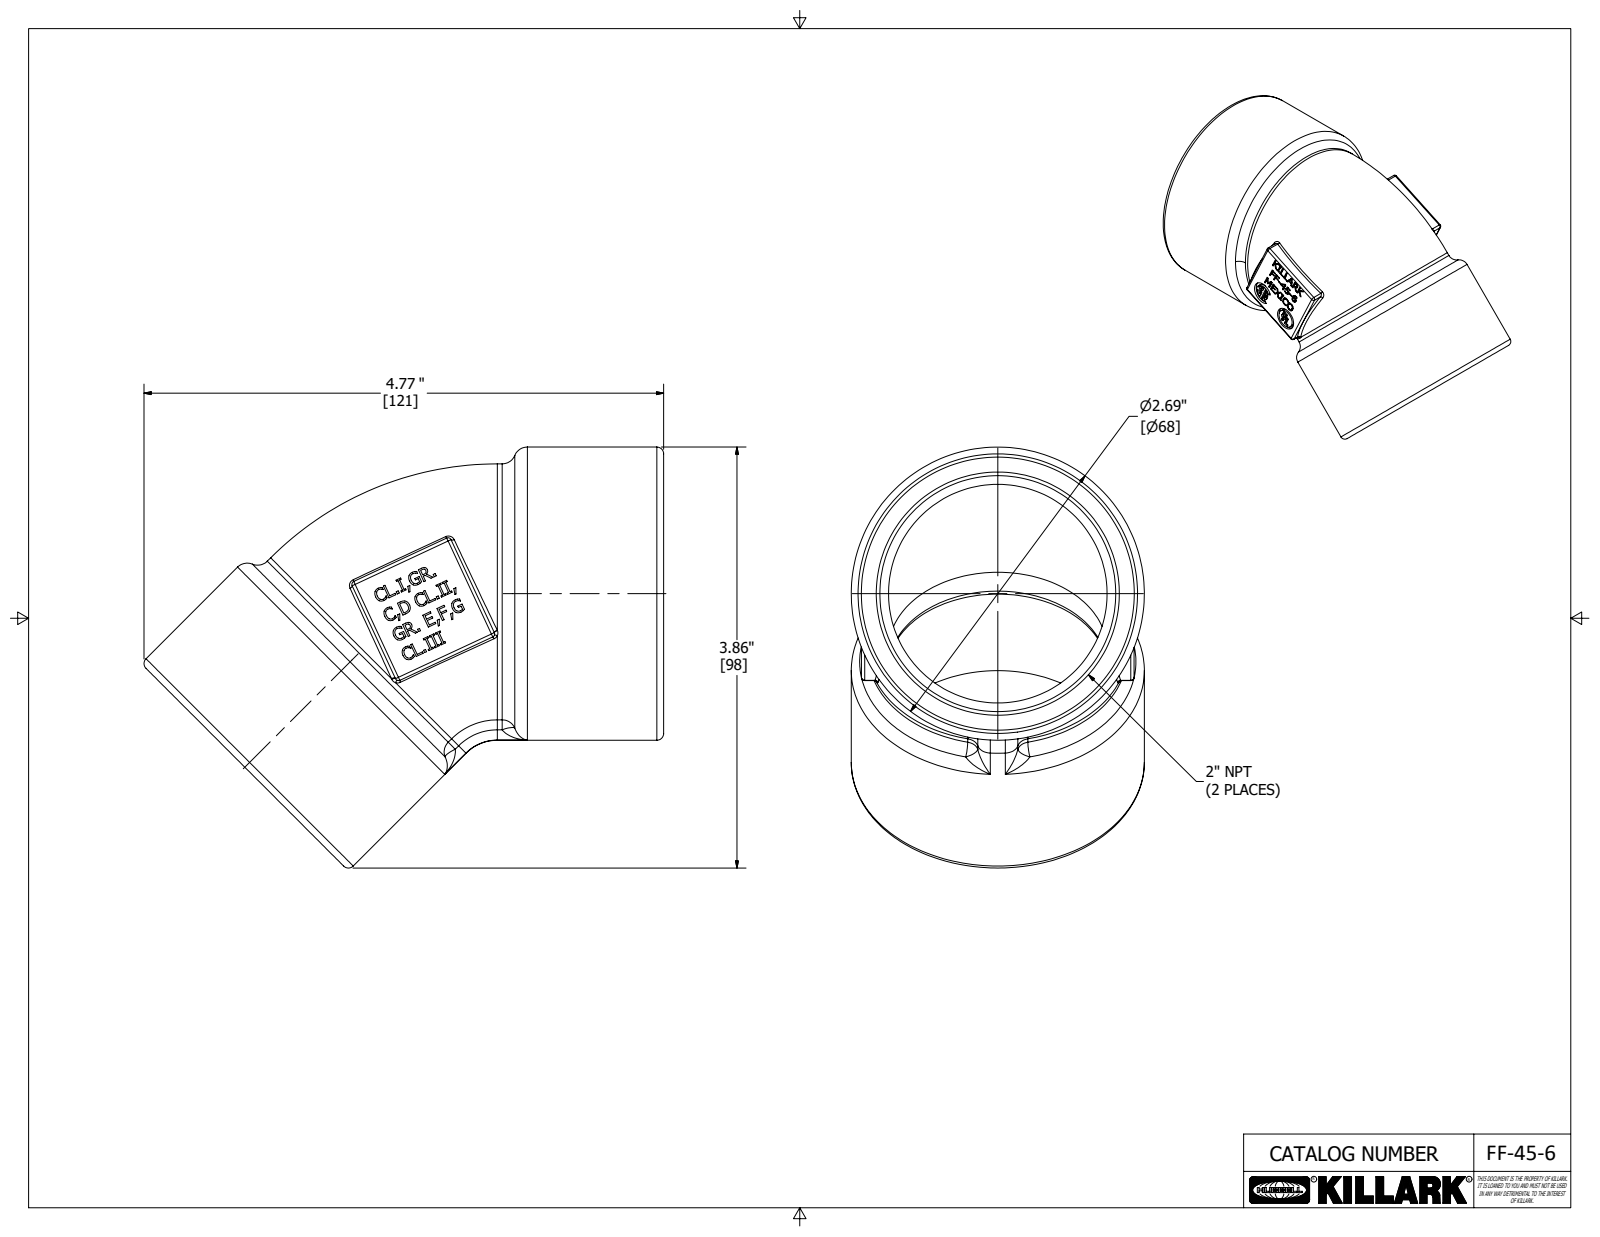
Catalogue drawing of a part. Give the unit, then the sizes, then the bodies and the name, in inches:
Units: inches
Overall size (bounding box): 4.765 × 3.859 × 2.688
Round holes (diameter × count): ⌀2.004 ×2, ⌀0.035 ×1, ⌀0.313 ×1
Round bosses / shafts (diameter × count): ⌀2.687 ×2, ⌀2.379 ×2, ⌀0.255 ×1, ⌀0.029 ×1
Partial cylindrical surfaces — rounded edges, fillets, slot ends (radius × count): R0.03 ×12, R0.125 ×8, R0.005 ×1, R0.01 ×1, R0.039 ×1, R0.071 ×1, R0.1 ×1, R0.117 ×1
Main face-to-face distances: 2.5, 1, 0.032, 2.468, 2.436, 0.198, 0.3, 0.078, 0.102, 0.014
Hole centre spacings: 0.076
Volume: 7.573 in³ · Surface area: 70.32 in²
Bodies: 1 solid, 818 faces (511 planar, 48 cylindrical, 259 other)
Part name (STEP PRODUCT): 18235-2
STEP written by: Autodesk Inventor 2020 (AUTOMOTIVE_DESIGN)
